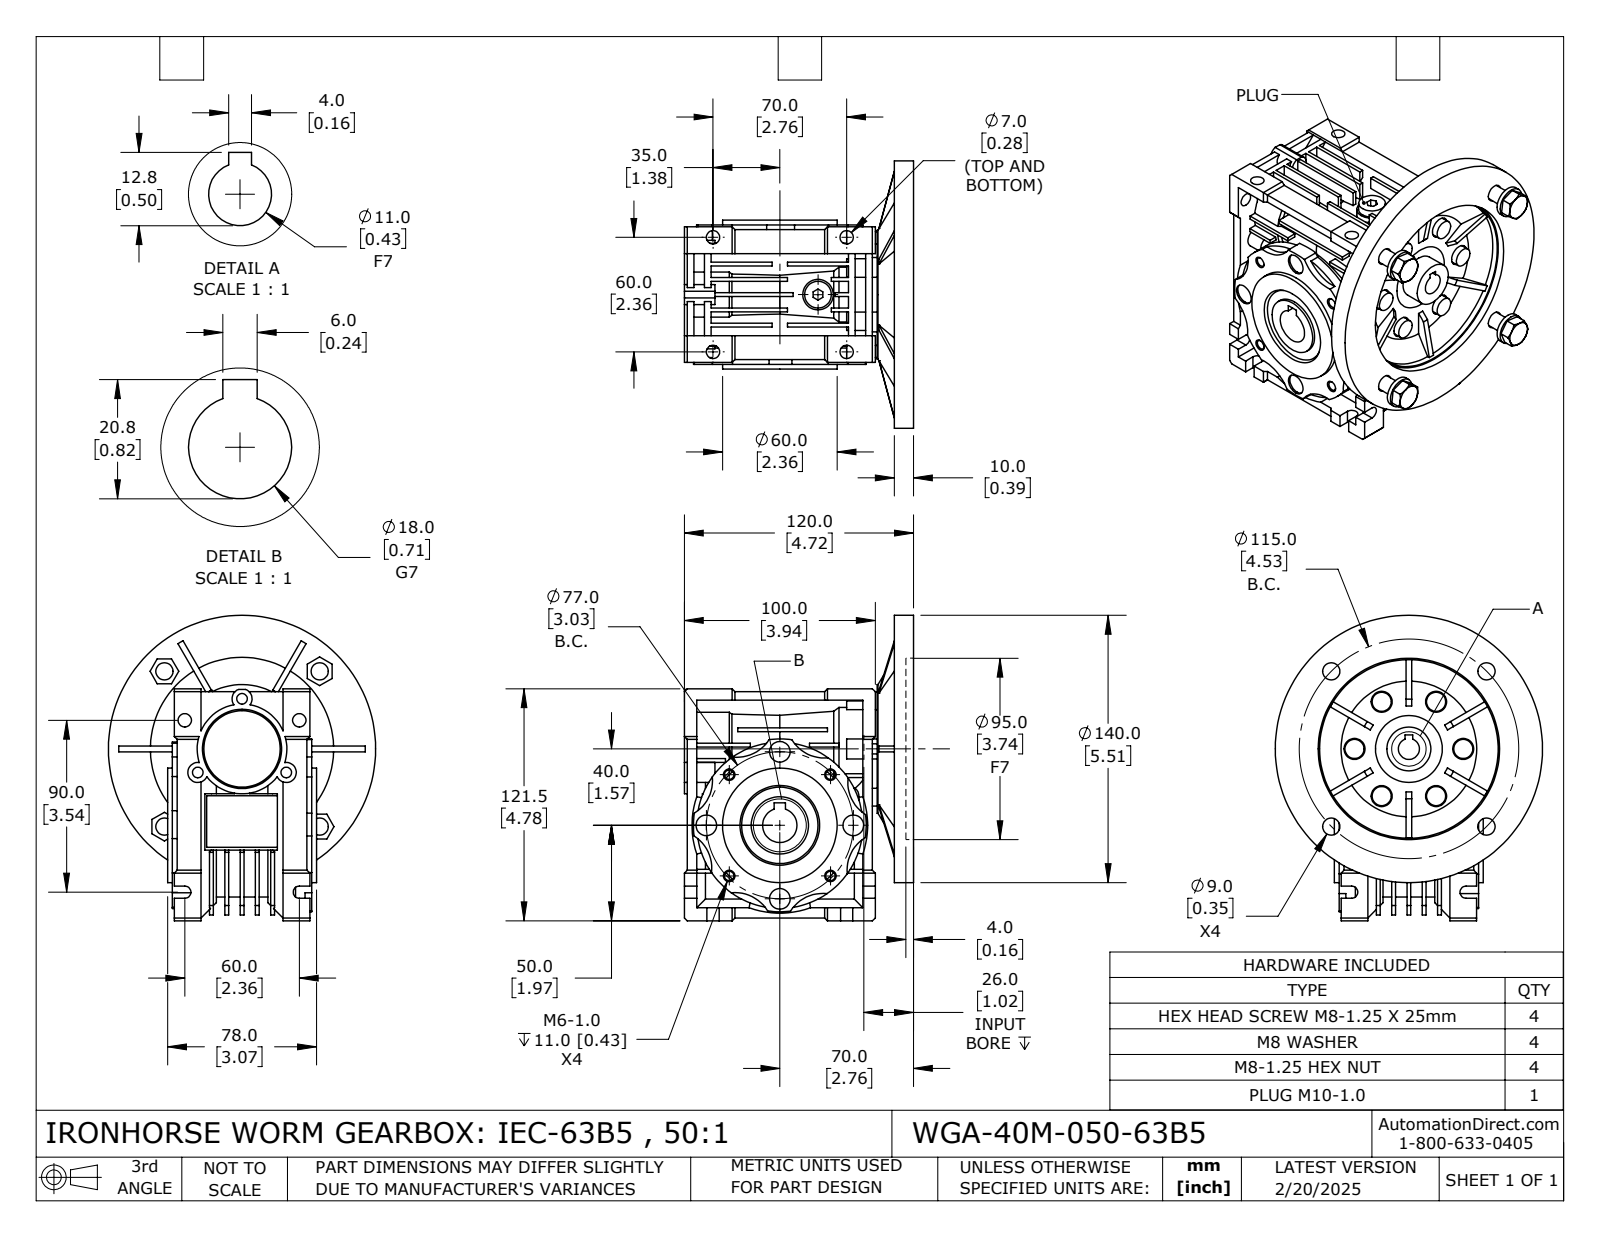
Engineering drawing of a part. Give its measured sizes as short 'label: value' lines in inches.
name: WGA-40M-050-63B5
written by: SolidWorks 2024 (CONFIG_CONTROL_DESIGN)
unit: in
bodies: 18 solids, 1083 faces (592 planar, 298 cylindrical, 193 other)
size: 6.299 × 5.512 × 5.432
volume: 45.77 in³; area: 295.5 in²
holes: 7× ⌀0.433, 6× ⌀0.276, 5× ⌀0.354, 4× ⌀0.194, 4× ⌀0.268, 4× ⌀0.315, 4× ⌀0.359, 4× ⌀0.425, 3× ⌀0.219, 1× ⌀0.453, 1× ⌀0.709, 1× ⌀0.906
bosses: 6× ⌀0.394, 5× ⌀0.63, 1× ⌀5.512, 1× ⌀2.953, 1× ⌀2.657, 1× ⌀2.362, 1× ⌀2.126, 1× ⌀1.85
rounds: 8× R0.787, 6× R0.126, 6× R0.206, 3× R0.207, 1× R1.713, 1× R1.716, 1× R1.781, 1× R1.811
face distances: 0.394, 0.315, 0.236, 0.079, 0.197, 0.059, 0.63, 0.945, 0.551, 0.098
hole spacings: 1.122, 1.146, 2.765, 1.943, 1.215, 1.32, 1.476, 1.516
